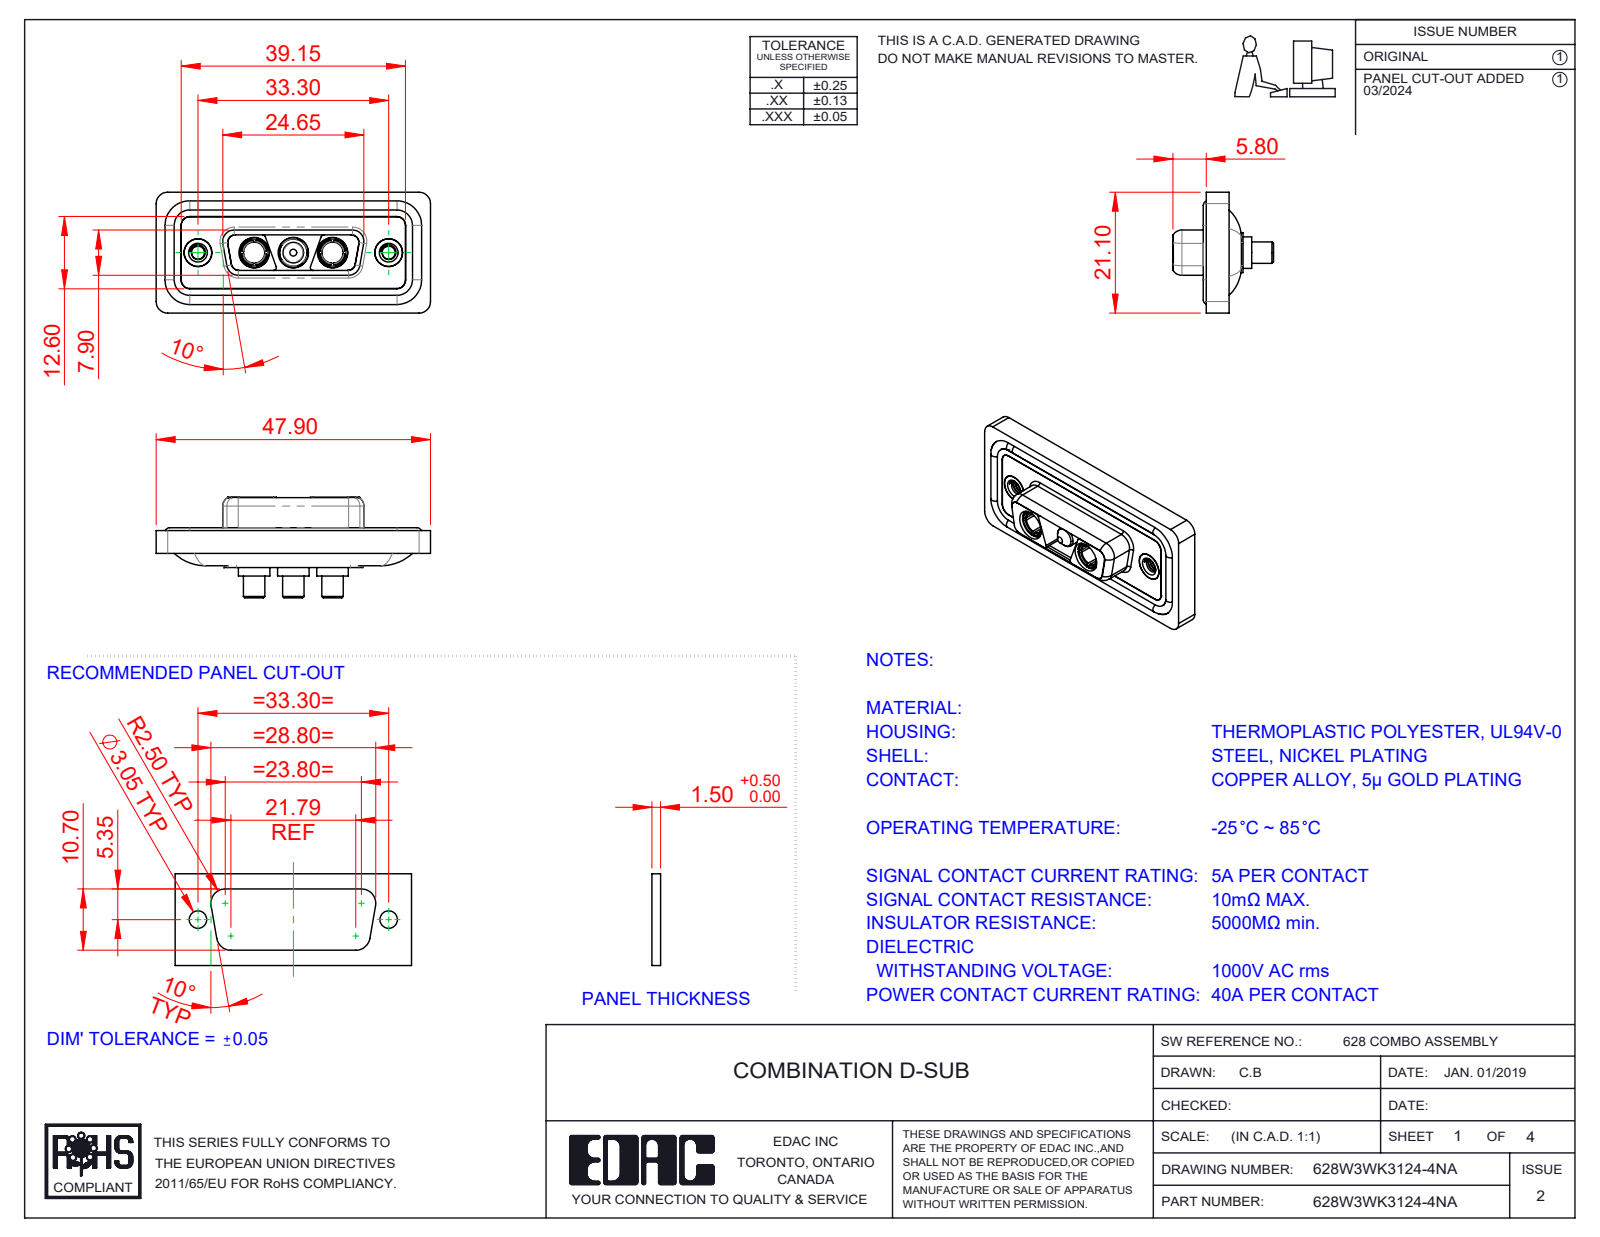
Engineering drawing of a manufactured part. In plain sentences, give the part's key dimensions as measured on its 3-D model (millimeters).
The part is named "628Combo Housing_3WK3; Power Socket_40A S; 628Combo Threaded Rivet_A; 628Combo Shell Front_15 Contacts (+4 more)". Its 3-D file was written by "SolidWorks 2023 (CONFIG_CONTROL_DESIGN)". It is 13 solids with 581 faces: 178 planar, 260 cylindrical and 143 other. Overall it measures 47.9 by 21.1 by 17.55 millimeters. Its volume is 5 935 cubic millimeters and its surface area 9 535 square millimeters. Round holes: 5 of diameter 4.85, 3 of diameter 5.3, 2 of diameter 2.26, 2 of diameter 3.7, 2 of diameter 4, 2 of diameter 4.05, 2 of diameter 5. Round bosses or shafts: 4 of diameter 1.6, 3 of diameter 5.5, 3 of diameter 5.2, 3 of diameter 4.75, 3 of diameter 3.75, 2 of diameter 4.96, 2 of diameter 4.95, 2 of diameter 4.8. Partial cylindrical surfaces (rounded edges, fillets, slot ends): 22 of radius 1.5, 20 of radius 2, 12 of radius 1.35, 8 of radius 0.5, 8 of radius 1.6, 4 of radius 0.25, 4 of radius 0.6, 4 of radius 0.65. The main face-to-face distances are 0.4, 1.6, 0.5, 1.8, 1.1, 2.9, 5.65, 7.05, 5.35, 1.5. The hole center spacings are 6.85, 9.8, 16.65, 23.5, 13.7, 33.3.
